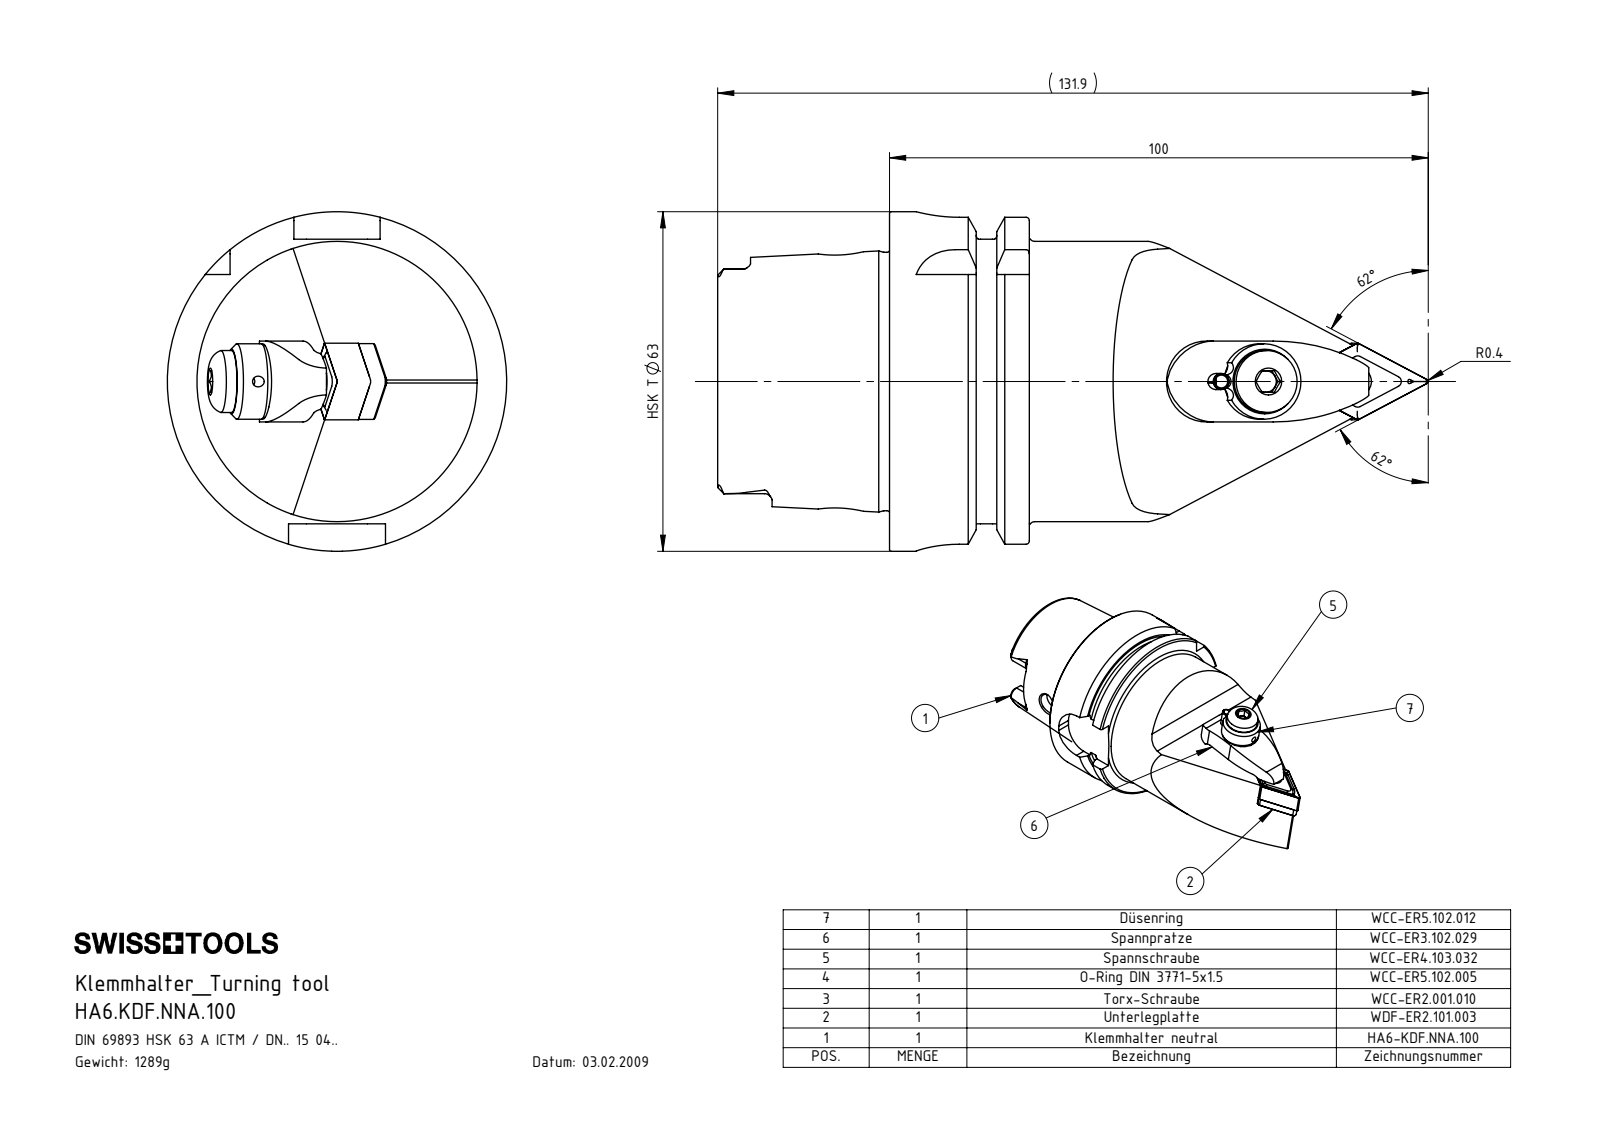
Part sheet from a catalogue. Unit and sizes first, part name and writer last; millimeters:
Units: millimetres
Overall size (bounding box): 131.9 × 63 × 63
Round holes (diameter × count): ⌀5 ×4, ⌀2 ×3, ⌀7 ×2, ⌀2.4 ×1, ⌀3 ×1, ⌀4.2 ×1, ⌀5.16 ×1, ⌀6 ×1, ⌀6.2 ×1, ⌀6.5 ×1, ⌀7.5 ×1, ⌀8.4 ×1
Round bosses / shafts (diameter × count): ⌀6 ×2, ⌀3 ×2, ⌀63 ×1, ⌀54.95 ×1, ⌀52 ×1, ⌀47.94 ×1, ⌀14 ×1, ⌀11.5 ×1
Partial cylindrical surfaces — rounded edges, fillets, slot ends (radius × count): R0.39 ×6, R0.4 ×6, R0.69 ×6, R1.4 ×6, R8 ×4, R1.5 ×3, R2 ×2, R2.82 ×2
Main face-to-face distances: 25.95, 16, 9.95, 11.89, 31.9, 41.85, 57.85, 6.05, 52.8, 21.8
Hole centre spacings: 8, 20, 28, 19.8, 7.99, 8.2, 8.21, 20.01
Volume: 165 184 mm³ · Surface area: 36 928 mm²
Bodies: 11 solids, 468 faces (124 planar, 156 cylindrical, 188 other)
Part name (STEP PRODUCT): WCC-ER4.103.032_A; HA6.KDF.NNA.100; DNMG150604; KVT_MB_600_060 (+7 more)
STEP written by: SolidWorks 2017 (AUTOMOTIVE_DESIGN)
